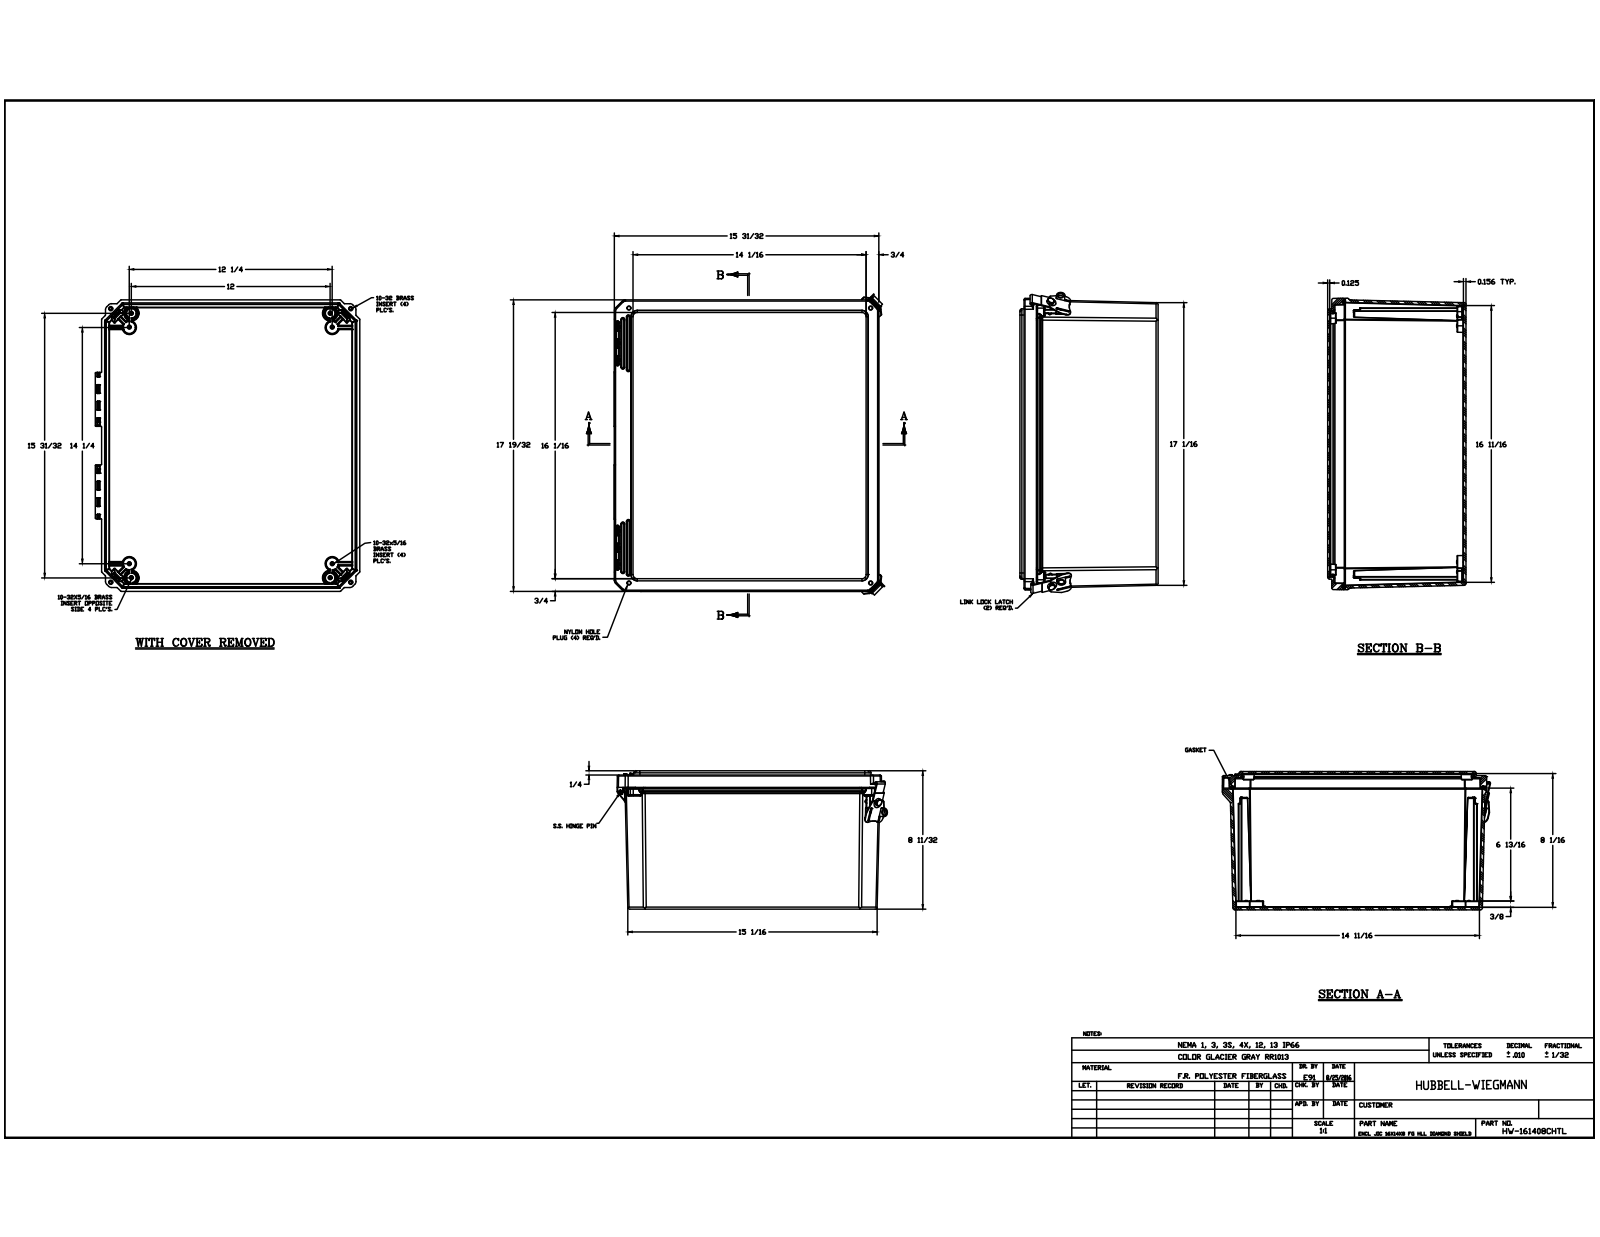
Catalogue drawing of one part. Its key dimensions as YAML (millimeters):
part_name: "HW-161408CHTL; DS161408BOX; BRASS INSERT-(; BRASS INSERT-(_1 (+6 more)"
step_written_by: "Autodesk Inventor 2017 (CONFIG_CONTROL_DESIGN)"
units: millimeters
bodies: {solids: 35, faces: 2347, planar: 811, cylindrical: 920, other: 616}
overall_size: [469.17, 416.67, 211.87]
volume: 3033000
surface_area: 1453000
round_holes:
  - {diameter: 3.96, count: 16}
  - {diameter: 3.86, count: 8}
  - {diameter: 2.49, count: 4}
  - {diameter: 3.81, count: 4}
  - {diameter: 6.4, count: 4}
  - {diameter: 6.43, count: 4}
  - {diameter: 1.27, count: 2}
  - {diameter: 3.05, count: 2}
  - {diameter: 5.56, count: 2}
  - {diameter: 5.77, count: 2}
  - {diameter: 7.94, count: 2}
  - {diameter: 9.22, count: 2}
round_bosses_or_shafts:
  - {diameter: 6.25, count: 16}
  - {diameter: 5.3, count: 4}
  - {diameter: 5.08, count: 4}
  - {diameter: 3.43, count: 3}
  - {diameter: 15.24, count: 2}
  - {diameter: 1.27, count: 2}
  - {diameter: 11.05, count: 1}
  - {diameter: 11.05, count: 1}
partial_cylinders:
  - {radius: 0.25, count: 195}
  - {radius: 0.13, count: 80}
  - {radius: 0.51, count: 57}
  - {radius: 0.76, count: 41}
  - {radius: 3.17, count: 34}
  - {radius: 0.99, count: 28}
  - {radius: 1.59, count: 26}
  - {radius: 0.76, count: 24}
face_to_face_distances: [3.17, 3.96, 207.91, 211.87, 208.7, 204.74, 4.56, 4.59, 6.35, 3.18]
hole_center_spacings: [20.14, 33.78, 308.74, 337.73, 342.1, 403.83, 414.64, 492.01]
